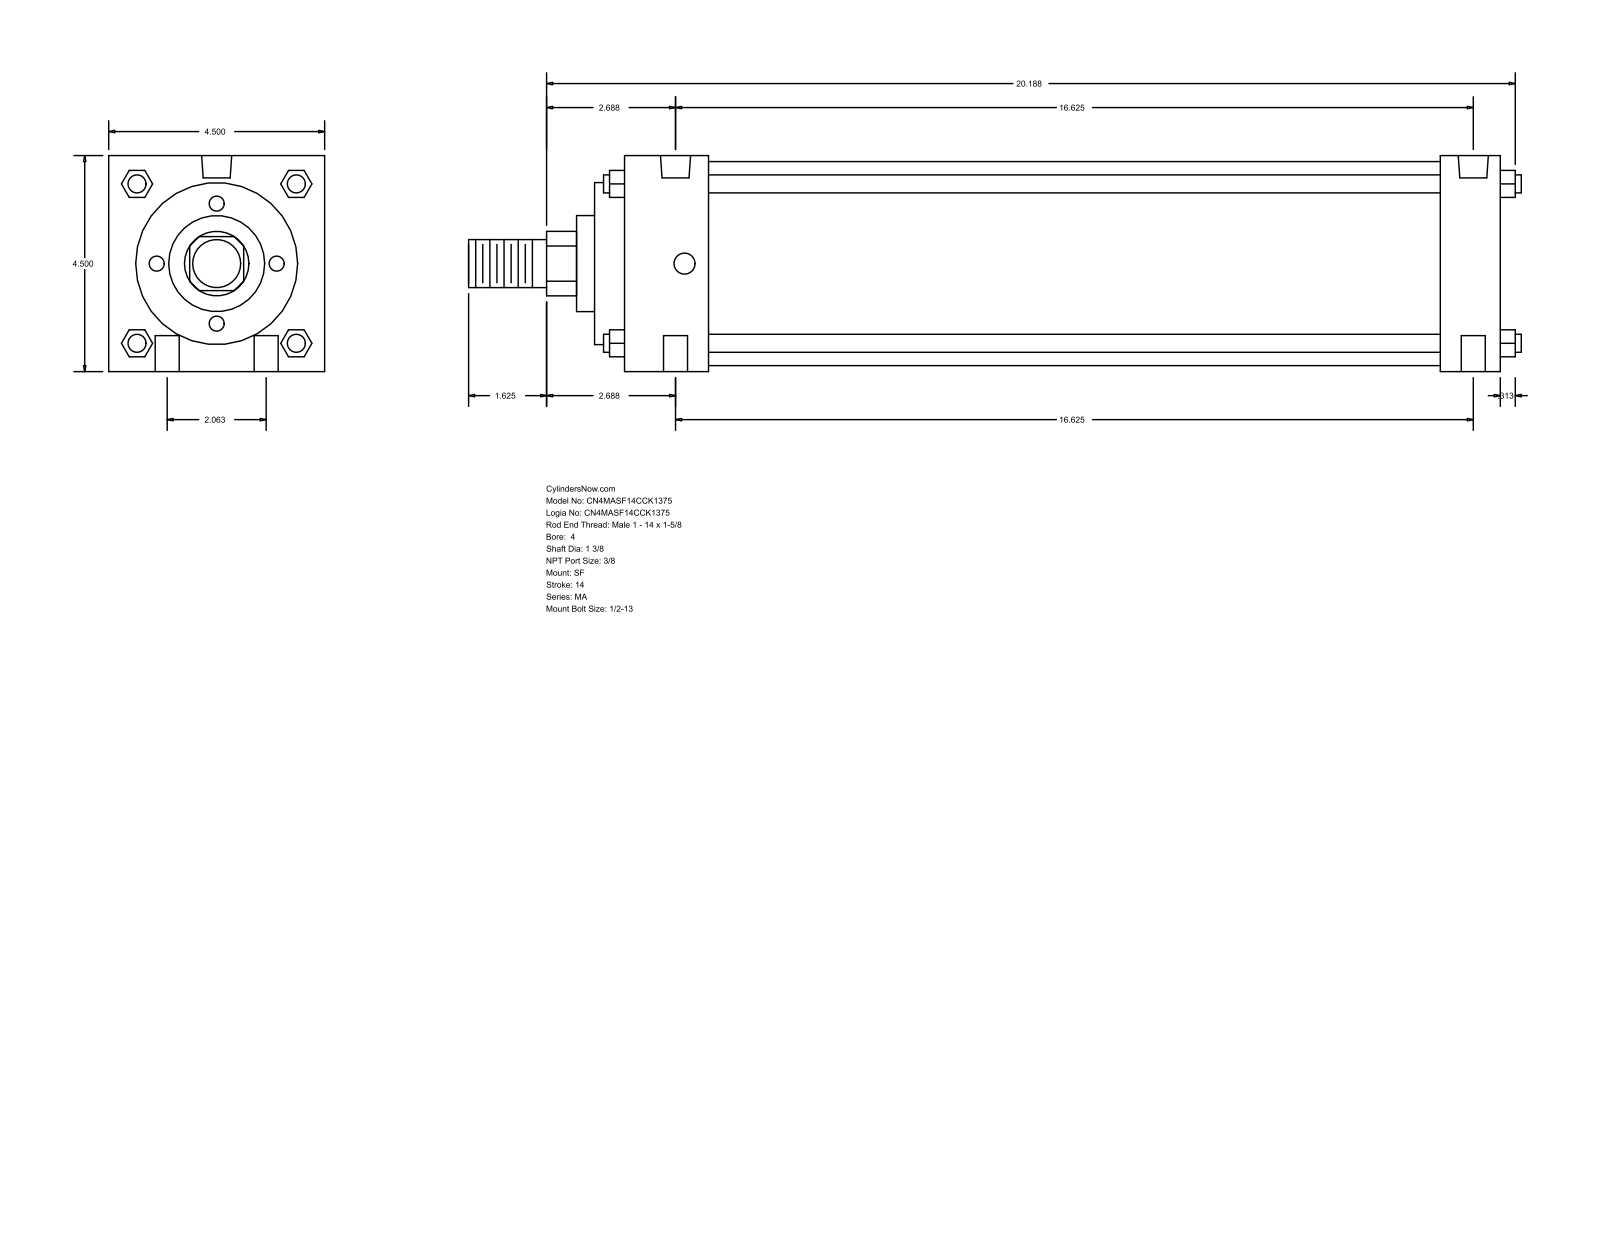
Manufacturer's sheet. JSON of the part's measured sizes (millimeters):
{"part_name": "MA_SF__0400_1.375", "step_written_by": "GSSL Pune (CONFIG_CONTROL_DESIGN)", "units": "millimeters", "bodies": {"solids": 0, "faces": 126, "planar": 95, "cylindrical": 31, "other": 0}, "overall_size": [557.21, 114.3, 114.3], "round_holes": [[12.7, 4], [11.11, 2], [15.93, 2]], "round_bosses_or_shafts": [[9.53, 4], [107.95, 1], [85.72, 1], [50.8, 1], [34.92, 1], [25.4, 1]], "partial_cylinders_radius": [[17.06, 1]], "face_to_face_distances": [114.3, 463.55, 479.42, 15.87, 447.67, 431.8, 31.75, 60.32, 44.45, 387.35], "hole_center_spacings": [26.19, 423.09, 422.28, 52.38, 425.52, 412.74]}
